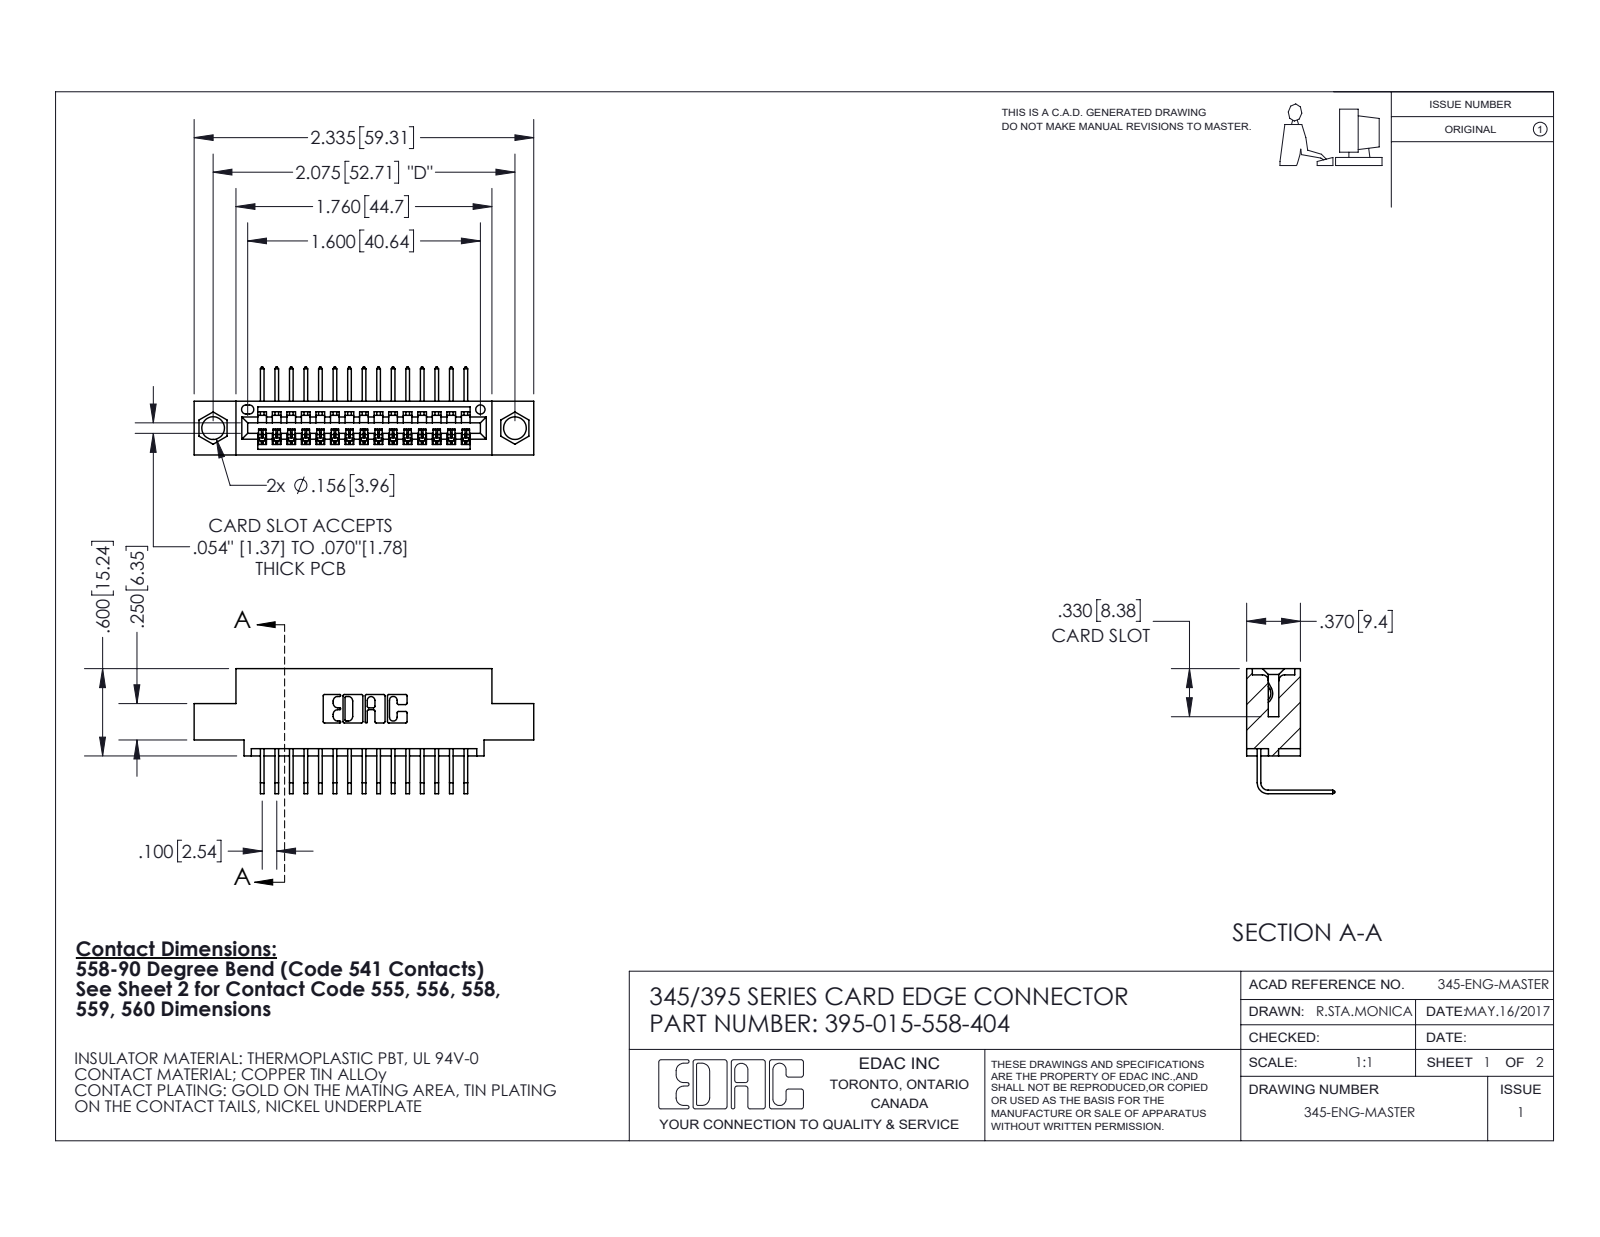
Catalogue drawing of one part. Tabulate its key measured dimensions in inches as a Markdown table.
| quantity | value |
| --- | --- |
| part name | 345 Part_0.110 Offset - 0.156 Dia-TI; 395-015-558-404; 345-292-001_558 Tail - 2 |
| STEP written by | SolidWorks 2020 (CONFIG_CONTROL_DESIGN) |
| units | inches |
| bodies | 16 solids, 1044 faces (728 planar, 316 cylindrical, 0 other) |
| overall size | 2.335 × 0.859 × 0.605 |
| volume | 0.322 in³ |
| surface area | 10.65 in² |
| round holes (diameter × count) | 0.156 × 2, 0.064 × 1 |
| partial cylindrical surfaces (radius × count) | 0.006 × 30, 0.01 × 22, 0.007 × 6, 0.031 × 6, 0.026 × 3, 0.031 × 2, 0.04 × 2, 0.014 × 1 |
| main face-to-face distances | 0.072, 0.298, 0.2, 0.37, 0.098, 0.272, 0.025, 0.1, 0.225, 0.16 |
| hole center spacings | 0.27, 1.842, 2.075 |
